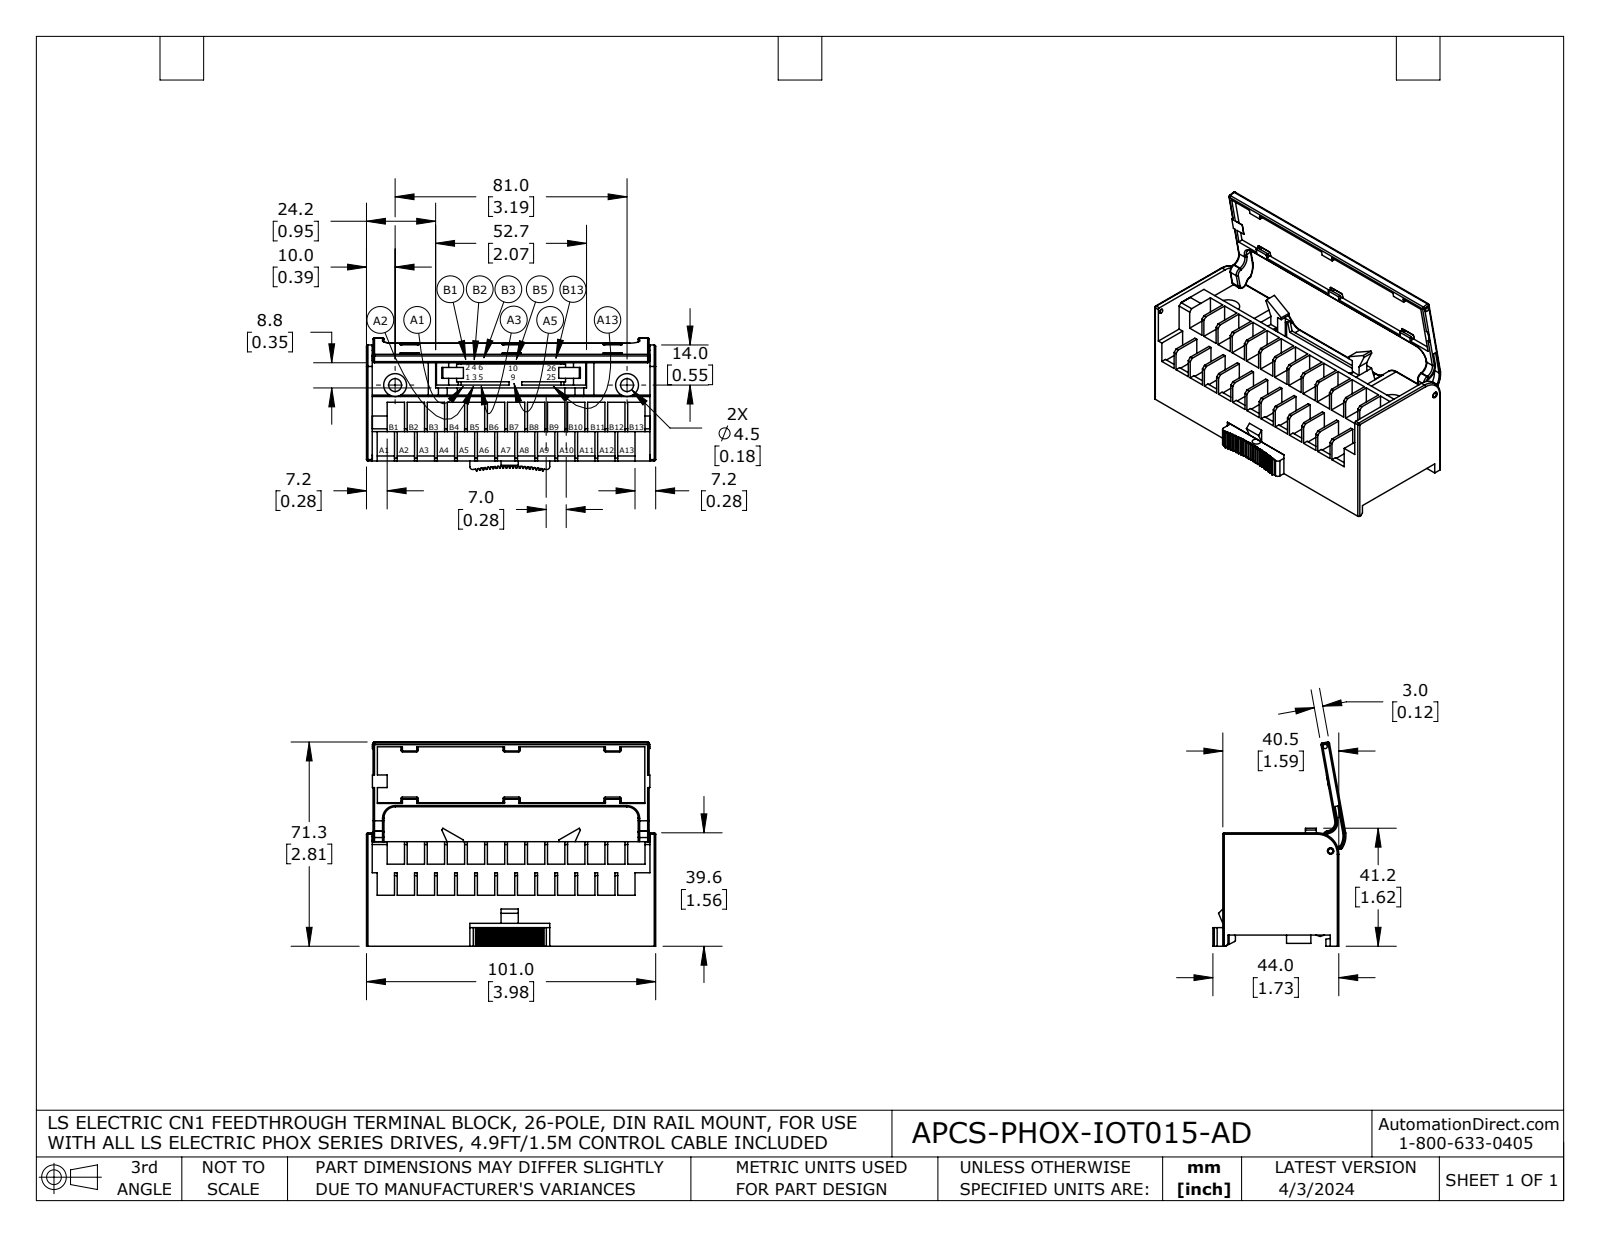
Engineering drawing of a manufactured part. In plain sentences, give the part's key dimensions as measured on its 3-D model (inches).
The part is named "APCS-PHOX-IOT015-AD". Its 3-D file was written by "SolidWorks 2021 (AUTOMOTIVE_DESIGN)". It is 2 solids with 694 faces: 458 planar, 175 cylindrical and 61 other. Overall it measures 3.976 by 1.731 by 1.622 inches. Its volume is 6.085 cubic inches and its surface area 53.63 square inches. Round holes: 2 of diameter 0.177, 2 of diameter 0.315, 1 of diameter 0.087, 1 of diameter 0.118. Round bosses or shafts: 2 of diameter 0.335, 1 of diameter 0.079, 1 of diameter 0.059. Partial cylindrical surfaces (rounded edges, fillets, slot ends): 67 of radius 0.02, 5 of radius 0.157, 4 of radius 0.039, 4 of radius 0.079, 4 of radius 0.197, 2 of radius 0.012, 2 of radius 0.016, 2 of radius 0.217. The main face-to-face distances are 0.059, 0.404, 1.594, 3.976, 0.551, 0.079, 0.974, 1.587, 0.118, 1.191. The hole center spacings are 1.882, 1.912, 3.189.
